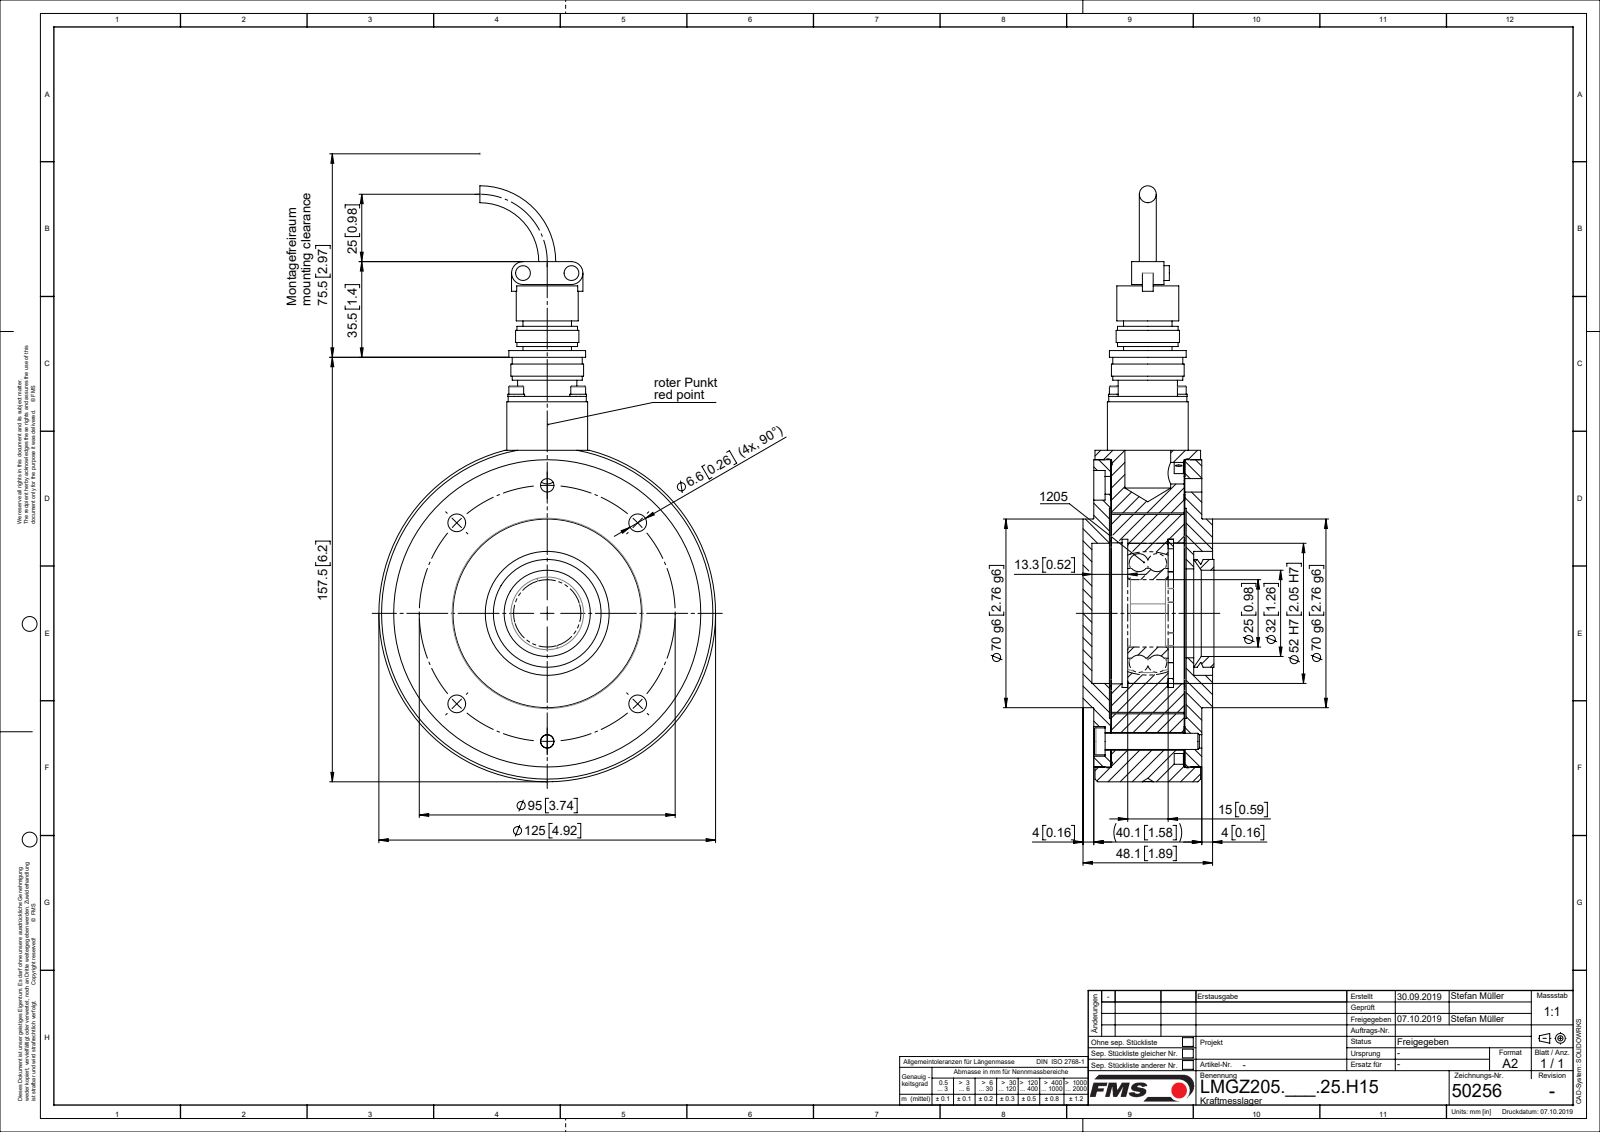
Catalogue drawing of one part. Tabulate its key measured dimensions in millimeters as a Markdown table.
| quantity | value |
| --- | --- |
| part name | ZEICHNUNG7; L50256; L4992504; L47956 (+8 more) |
| STEP written by | Mechanical Desktop 2007 (CONFIG_CONTROL_DESIGN) |
| units | millimeters |
| bodies | 19 solids, 374 faces (105 planar, 229 cylindrical, 40 other) |
| overall size | 221.15 × 125 × 48.1 |
| volume | 480 978 mm³ |
| surface area | 142 586 mm² |
| round holes (diameter × count) | 6.6 × 6, 3.2 × 4, 3.4 × 4, 5 × 2, 11 × 2, 23 × 1, 25 × 1, 31 × 1, 33 × 1, 37.9 × 1, 46 × 1, 52 × 1 |
| round bosses / shafts (diameter × count) | 5.5 × 6, 6.2 × 4, 3 × 4, 2.5 × 4, 125 × 1, 114 × 1, 70 × 1, 39 × 1 |
| partial cylindrical surfaces (radius × count) | 5 × 8, 4.25 × 2, 40.5 × 1, 47 × 1 |
| main face-to-face distances | 27.25, 33.55, 6.3, 6.55, 33.8, 27, 27.5, 4, 10.55, 37.8 |
| hole center spacings | 47.5, 16.26, 23, 36.36, 67.18, 87.77, 32.53, 95.01 |
